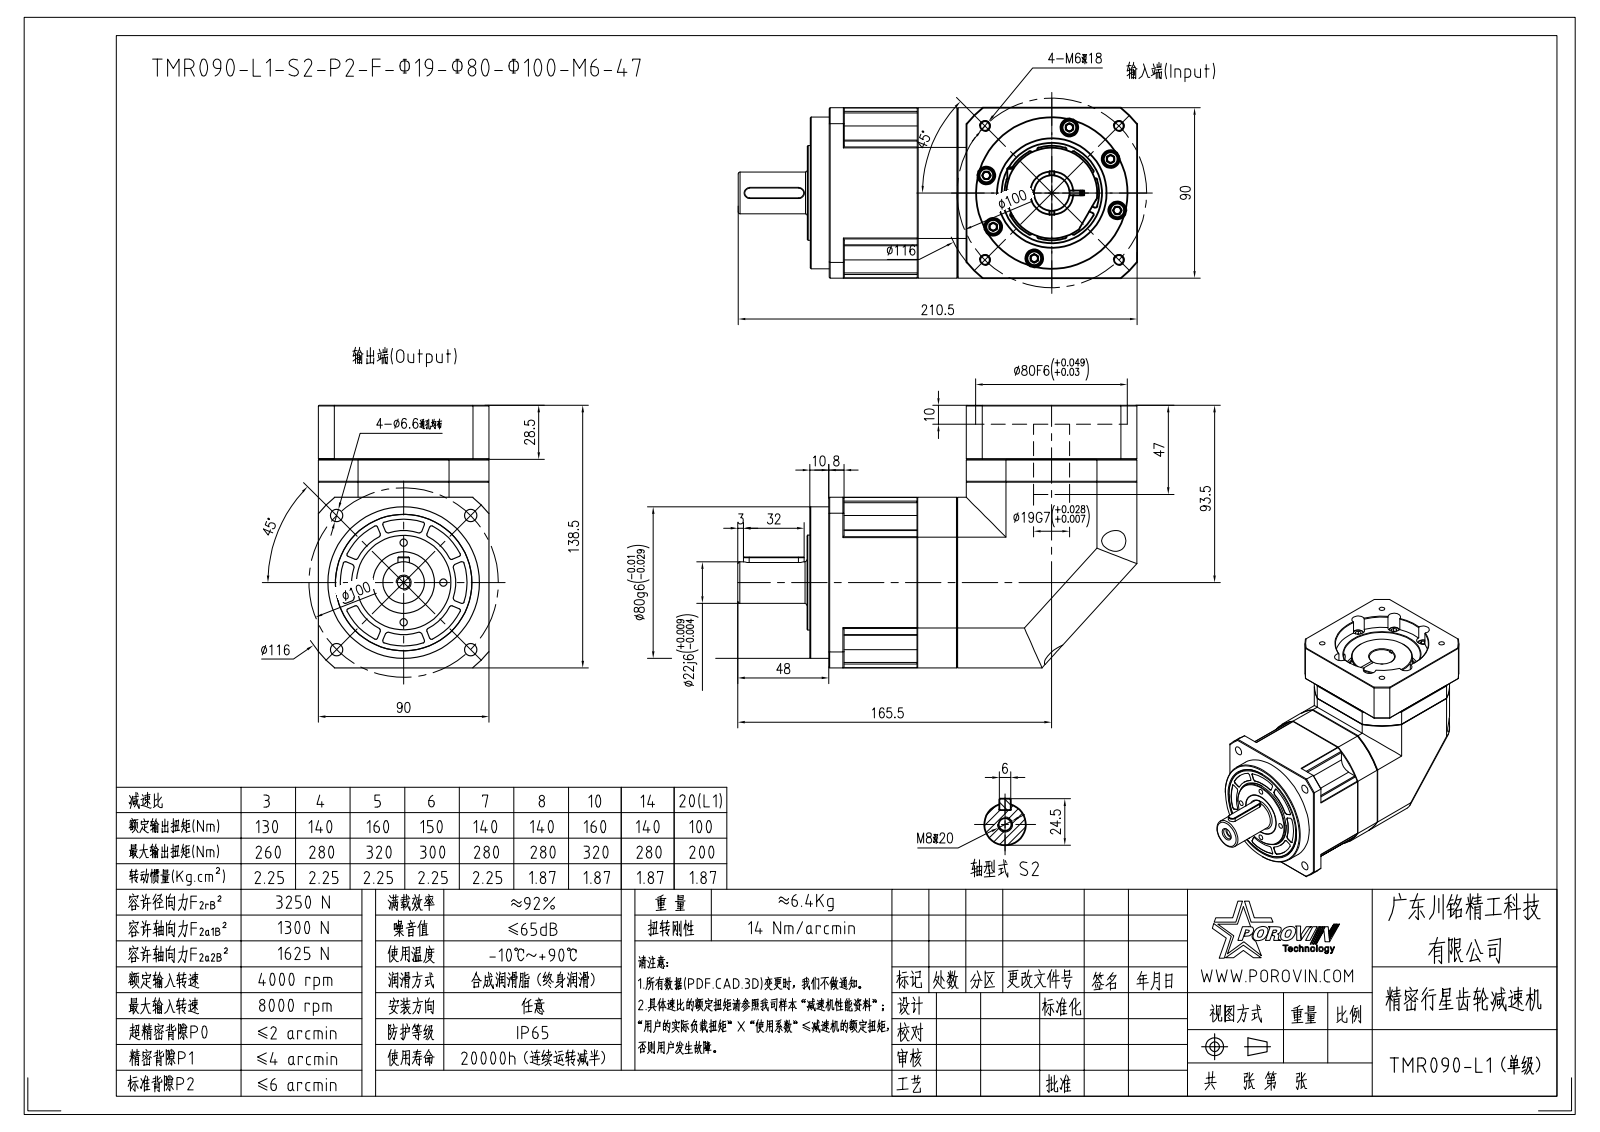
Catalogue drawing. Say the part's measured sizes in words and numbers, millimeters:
The part is named "HEXAGON_SOCKET_HEAD_CAP_S-25119; SPRING_LOCK_WASHERS--NORM-25005; SPRING_LOCK_WASHERS--NORM-14355; MR900001 (+8 more)". Its 3-D file was written by "CREO PARAMETRIC BY PTC INC, 2020053 (CONFIG_CONTROL_DESIGN)". It is 42 solids with 1283 faces: 512 planar, 545 cylindrical and 226 other. Overall it measures 210.5 by 138.5 by 90 millimeters. Its volume is 1 335 000 cubic millimeters and its surface area 210 656 square millimeters. Round holes: 12 of diameter 5.4, 12 of diameter 5.5, 12 of diameter 9.5, 7 of diameter 4.2, 5 of diameter 5, 5 of diameter 6.5, 4 of diameter 4, 4 of diameter 6.6, 4 of diameter 6.68, 4 of diameter 11, 1 of diameter 6.8, 1 of diameter 8.4. Round bosses or shafts: 12 of diameter 8.5, 12 of diameter 8, 12 of diameter 5, 4 of diameter 10, 4 of diameter 9.88, 4 of diameter 6, 1 of diameter 80, 1 of diameter 78. Partial cylindrical surfaces (rounded edges, fillets, slot ends): 92 of radius 1, 4 of radius 7.5, 3 of radius 51, 2 of radius 3, 2 of radius 58, 1 of radius 4, 1 of radius 5.25, 1 of radius 40. The main face-to-face distances are 90, 12, 21.3, 21.5, 10, 26, 110, 31.3, 98, 2.5. The hole center spacings are 35.75, 27.36, 38.16, 50.01, 66.06, 66.53, 70.72, 18.03.
